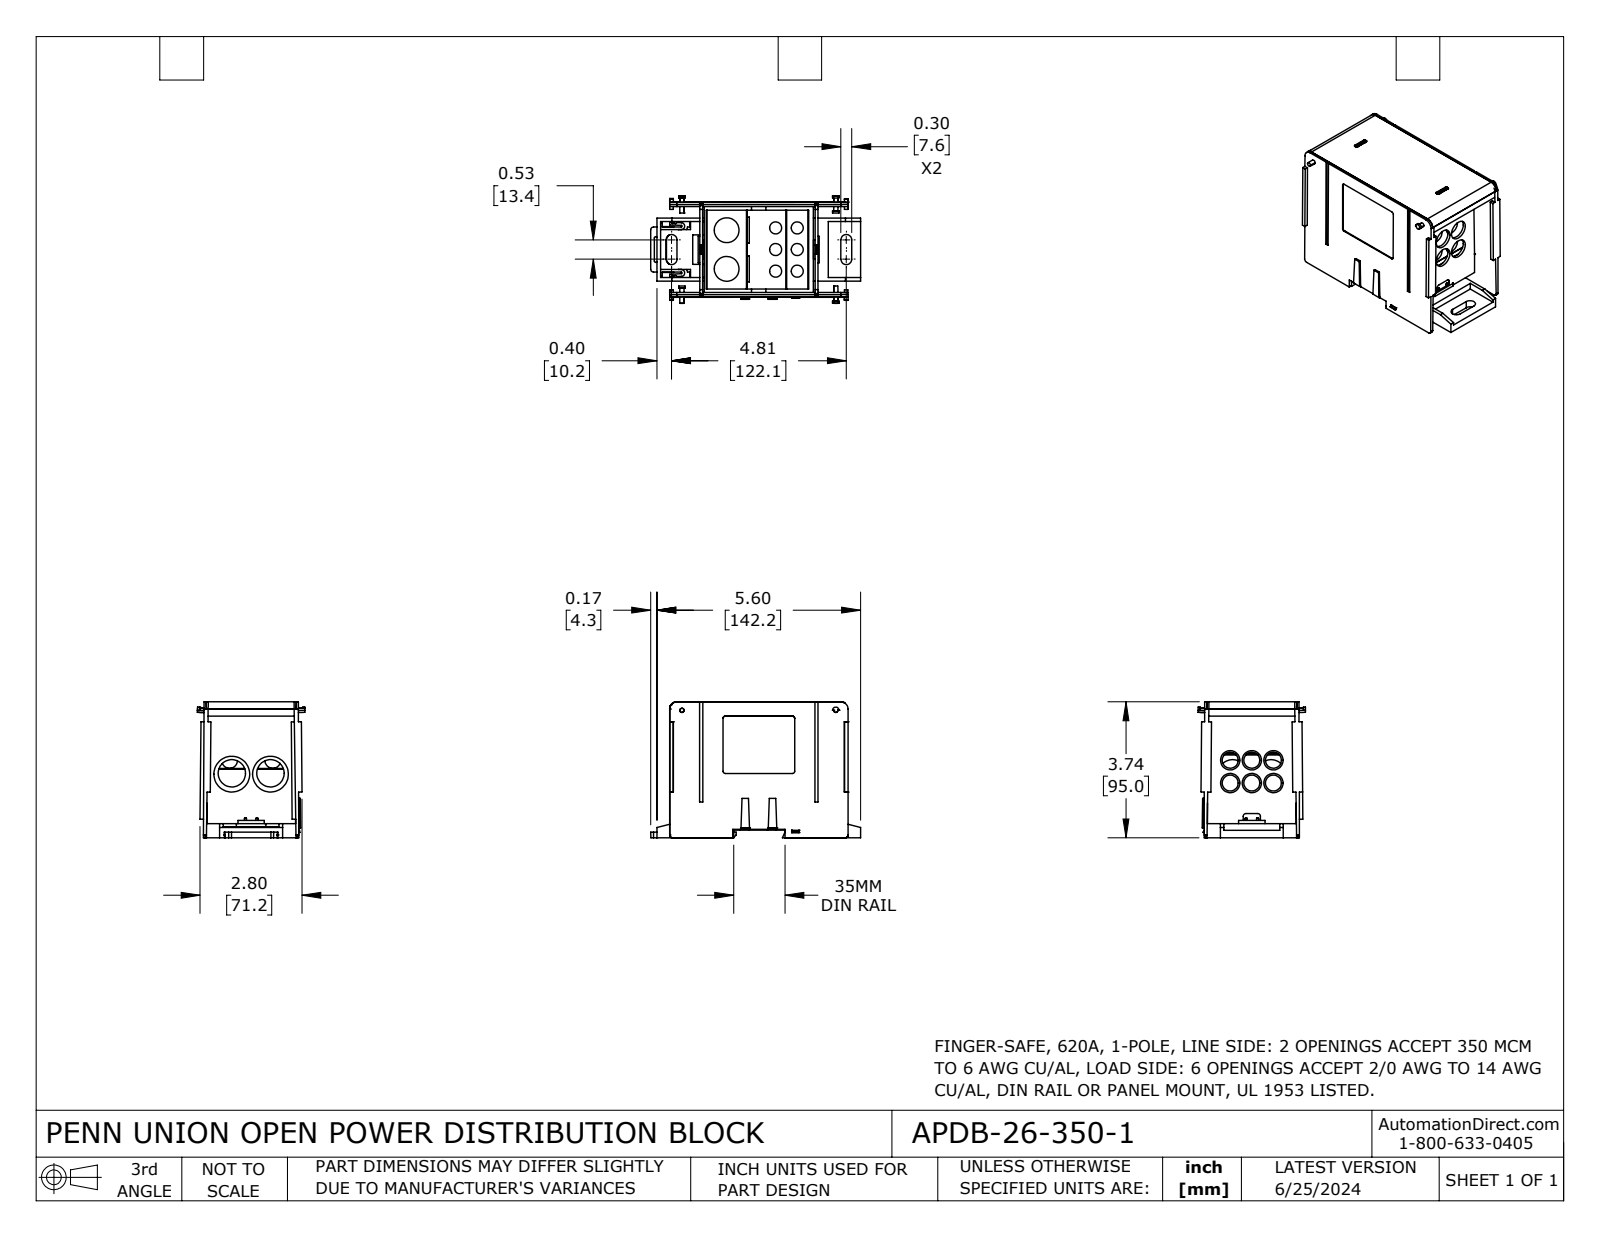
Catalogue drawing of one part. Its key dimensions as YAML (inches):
part_name: "APDB-26-350-1"
step_written_by: "SolidWorks 2023 (CONFIG_CONTROL_DESIGN)"
units: inches
bodies: {solids: 11, faces: 814, planar: 559, cylindrical: 182, other: 73}
overall_size: [5.77, 3.741, 2.955]
volume: 18.84
surface_area: 234.2
round_holes:
  - {diameter: 0.437, count: 6}
  - {diameter: 0.531, count: 6}
  - {diameter: 0.33, count: 5}
  - {diameter: 0.682, count: 2}
  - {diameter: 0.752, count: 2}
  - {diameter: 0.984, count: 2}
  - {diameter: 0.213, count: 1}
  - {diameter: 0.33, count: 1}
partial_cylinders:
  - {radius: 0.02, count: 32}
  - {radius: 0.059, count: 18}
  - {radius: 0.039, count: 10}
  - {radius: 0.079, count: 10}
  - {radius: 0.197, count: 10}
  - {radius: 0.012, count: 6}
  - {radius: 0.089, count: 4}
  - {radius: 0.15, count: 4}
face_to_face_distances: [0.079, 3.169, 2.54, 0.071, 2.469, 0.02, 0.177, 3.248, 3.091, 1.201]
hole_center_spacings: [0.594, 1.189, 0.839, 0.863, 0.593, 0.626, 1.063, 0.024]
